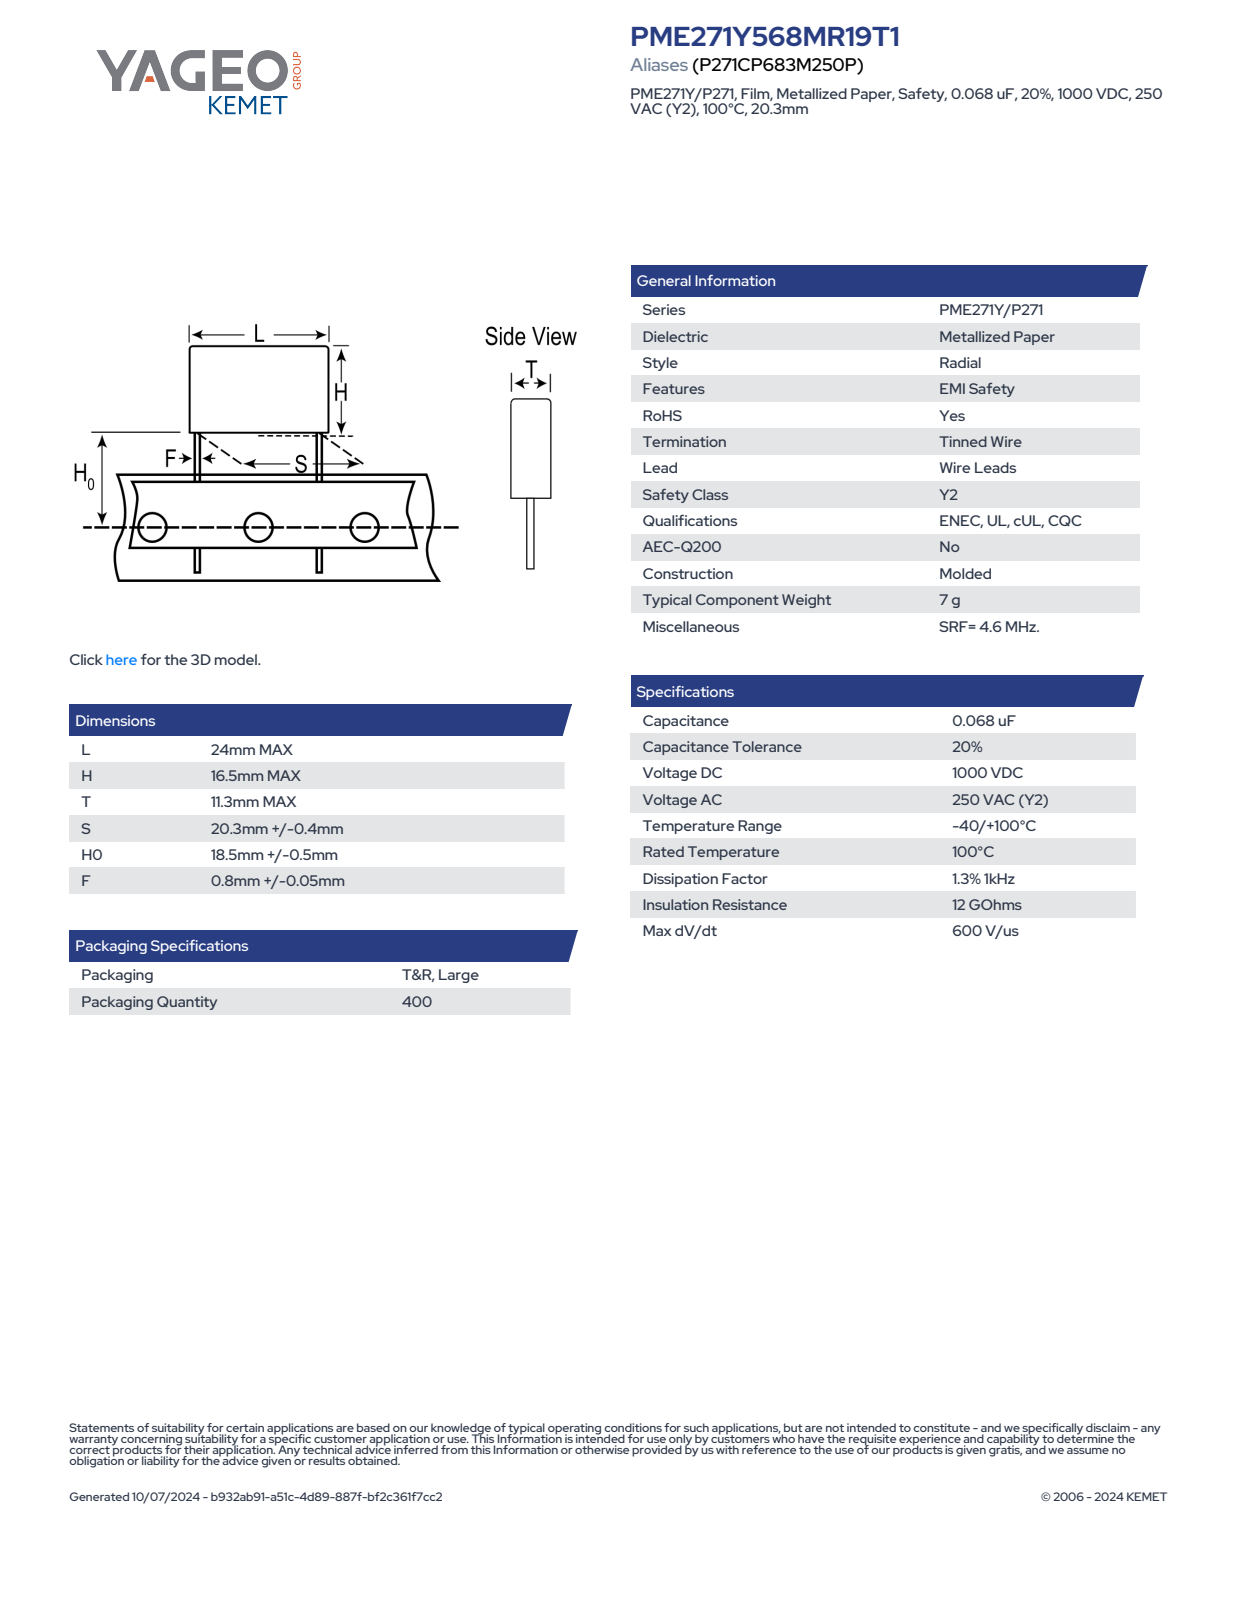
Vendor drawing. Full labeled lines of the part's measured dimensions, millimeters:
Part name (STEP PRODUCT): CFR_MOLDED_24X16.5X11.3_L24H16.5T11.3S20.3H019F0.85
STEP written by: SolidWorks 2014 (AUTOMOTIVE_DESIGN)
Units: millimetres
Bodies: 4 solids, 73 faces (65 planar, 8 cylindrical, 0 other)
Overall size (bounding box): 35.5 × 24 × 11.3
Volume: 4 493 mm³ · Surface area: 1 821 mm²
Round bosses / shafts (diameter × count): ⌀0.85 ×2
Partial cylindrical surfaces — rounded edges, fillets, slot ends (radius × count): R0.5 ×4
Main face-to-face distances: 11.3, 16.5, 24, 11.31, 19, 35.5, 28.07, 9.07, 7.43, 25.92
